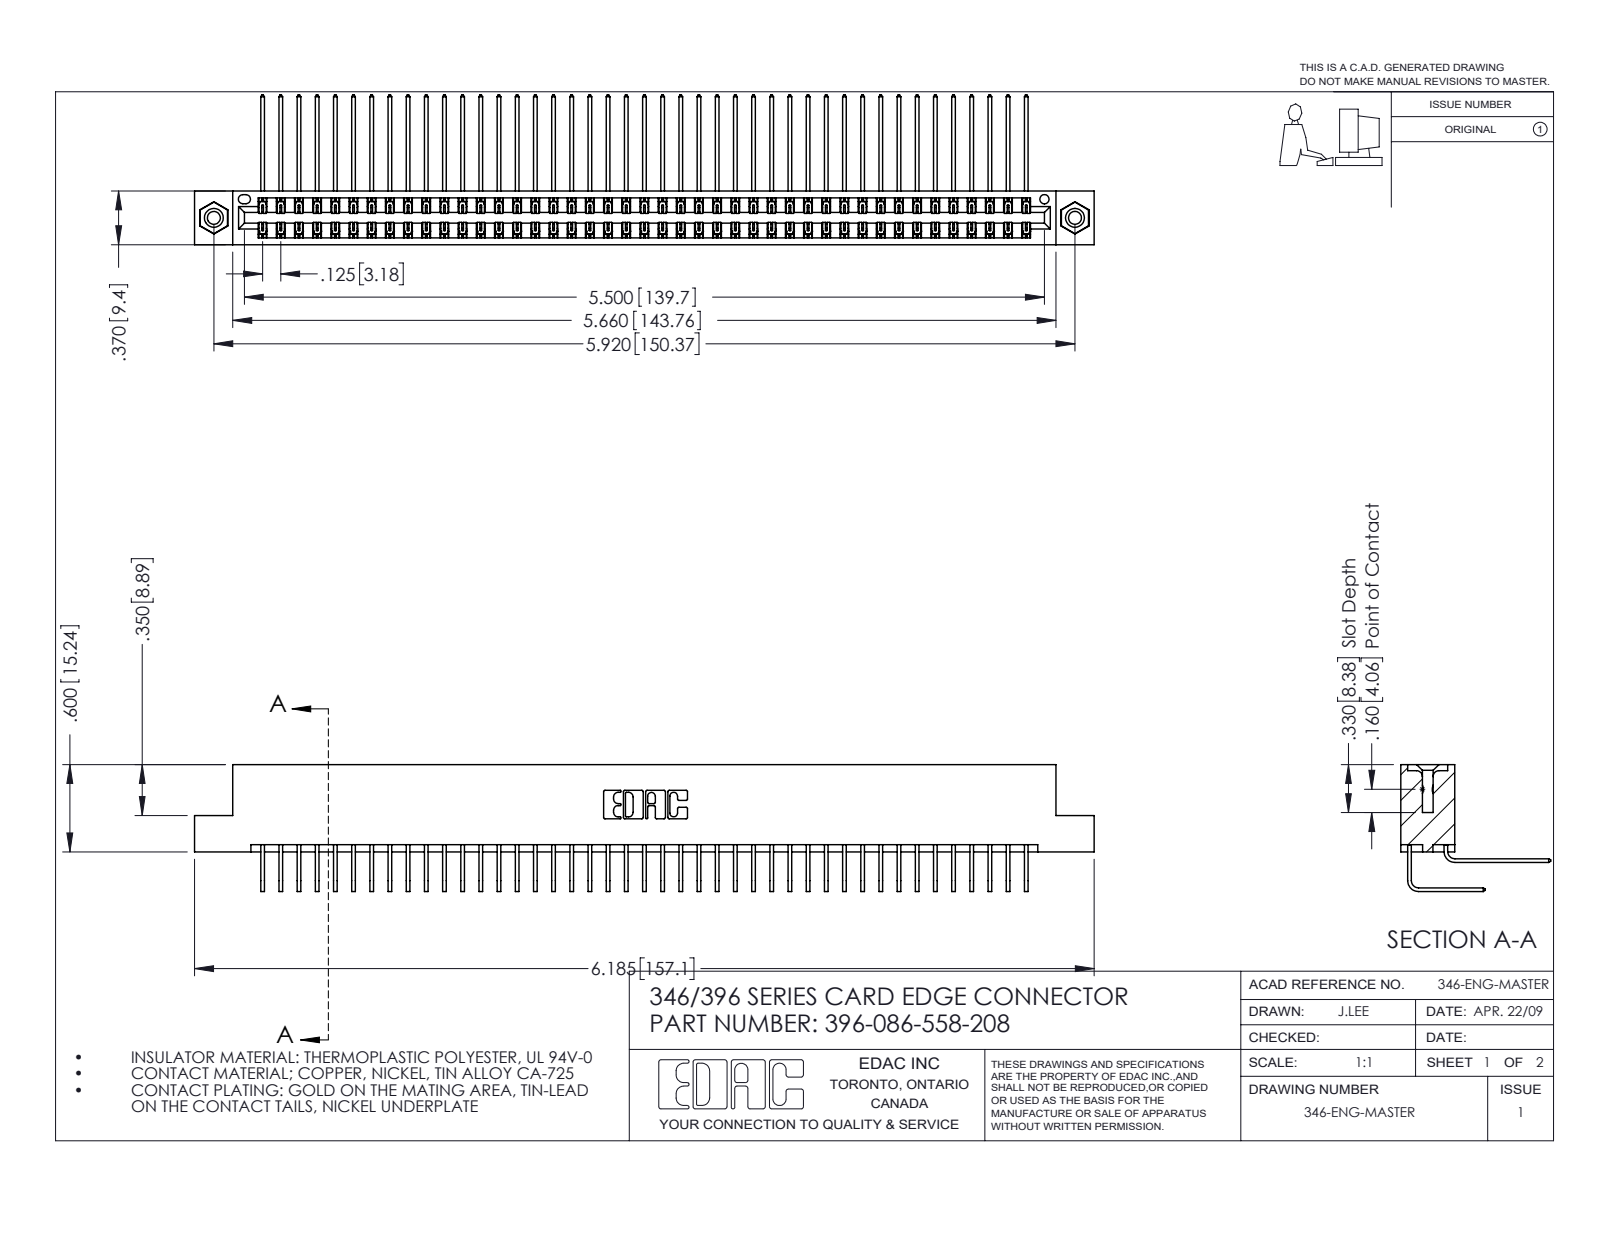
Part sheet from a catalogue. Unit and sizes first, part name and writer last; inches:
Units: inches
Overall size (bounding box): 6.185 × 1.03 × 0.873
Round holes (diameter × count): ⌀0.089 ×2, ⌀0.125 ×2, ⌀0.156 ×2, ⌀0.064 ×1
Round bosses / shafts (diameter × count): ⌀0.155 ×2
Partial cylindrical surfaces — rounded edges, fillets, slot ends (radius × count): R0.006 ×129, R0.01 ×22, R0.007 ×6, R0.031 ×6, R0.026 ×3, R0.014 ×2, R0.022 ×2, R0.024 ×2
Main face-to-face distances: 0.048, 0.322, 0.025, 0.37, 0.25, 0.072, 0.298, 0.275, 0.148, 0.222
Hole centre spacings: 0.246, 5.711, 5.92
Volume: 0.965 in³ · Surface area: 37.44 in²
Bodies: 89 solids, 4826 faces (3290 planar, 1520 cylindrical, 16 other)
Part name (STEP PRODUCT): 345-292-001_558 559 Tail - 1; 345-292-001_558 Tail - 2; 346 Part_Flush Mounting Lugs - 0.156 Dia-TI; 396-086-558-208 (+1 more)
STEP written by: SolidWorks 2016 (CONFIG_CONTROL_DESIGN)
